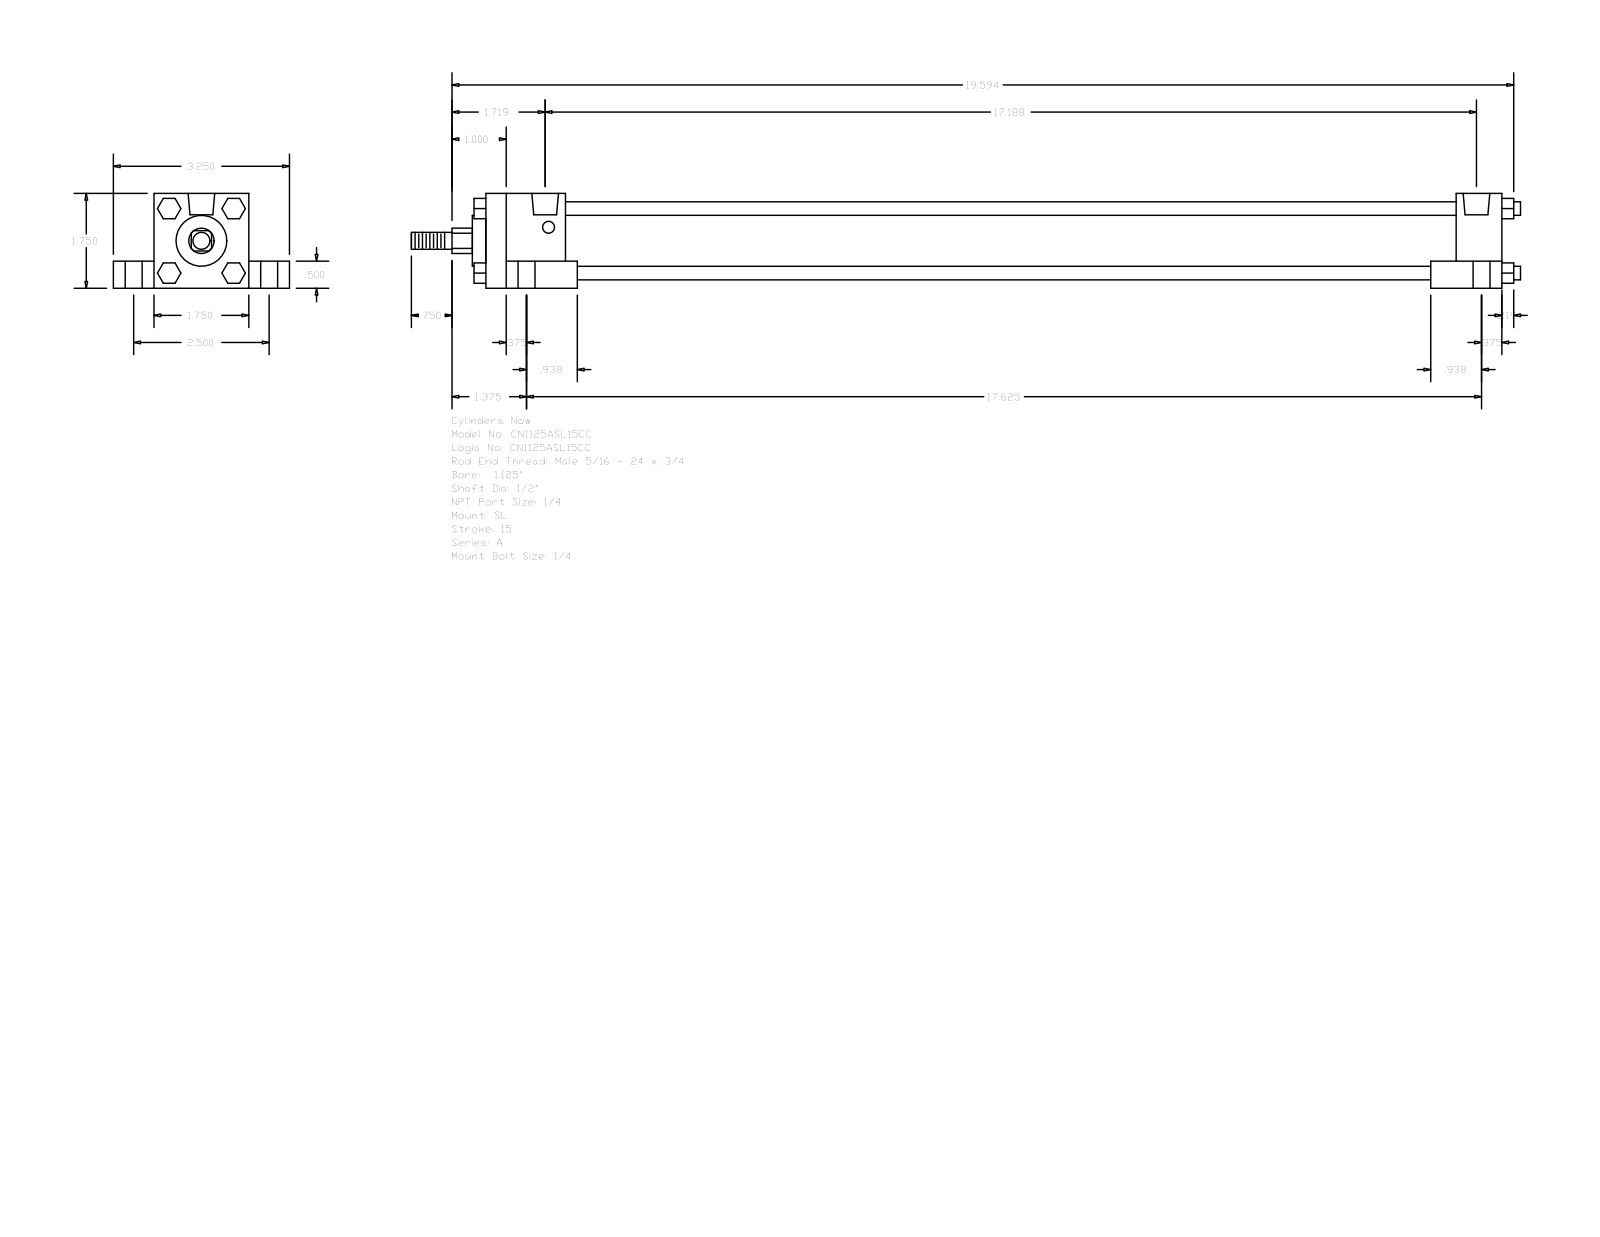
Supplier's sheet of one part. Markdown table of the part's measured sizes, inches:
| quantity | value |
| --- | --- |
| part name | A_SL__0112_0.5 |
| STEP written by | GSSL Pune (CONFIG_CONTROL_DESIGN) |
| units | inches |
| bodies | 0 solids, 150 faces (114 planar, 36 cylindrical, 0 other) |
| overall size | 20.469 × 3.25 × 1.75 |
| round holes (diameter × count) | 0.219 × 4, 0.313 × 4, 0.563 × 4, 0.492 × 2 |
| round bosses / shafts (diameter × count) | 0.25 × 4, 1.255 × 1, 0.937 × 1, 0.5 × 1, 0.313 × 1 |
| partial cylindrical surfaces (radius × count) | 0.234 × 1 |
| main face-to-face distances | 1.75, 1.25, 0.5, 0.75, 2.5, 17.281, 18.75, 17.906, 0.844, 1.469 |
| hole center spacings | 1.254, 1.26, 1.296, 1.315, 2.5, 17.063, 17.264, 17.326 |
